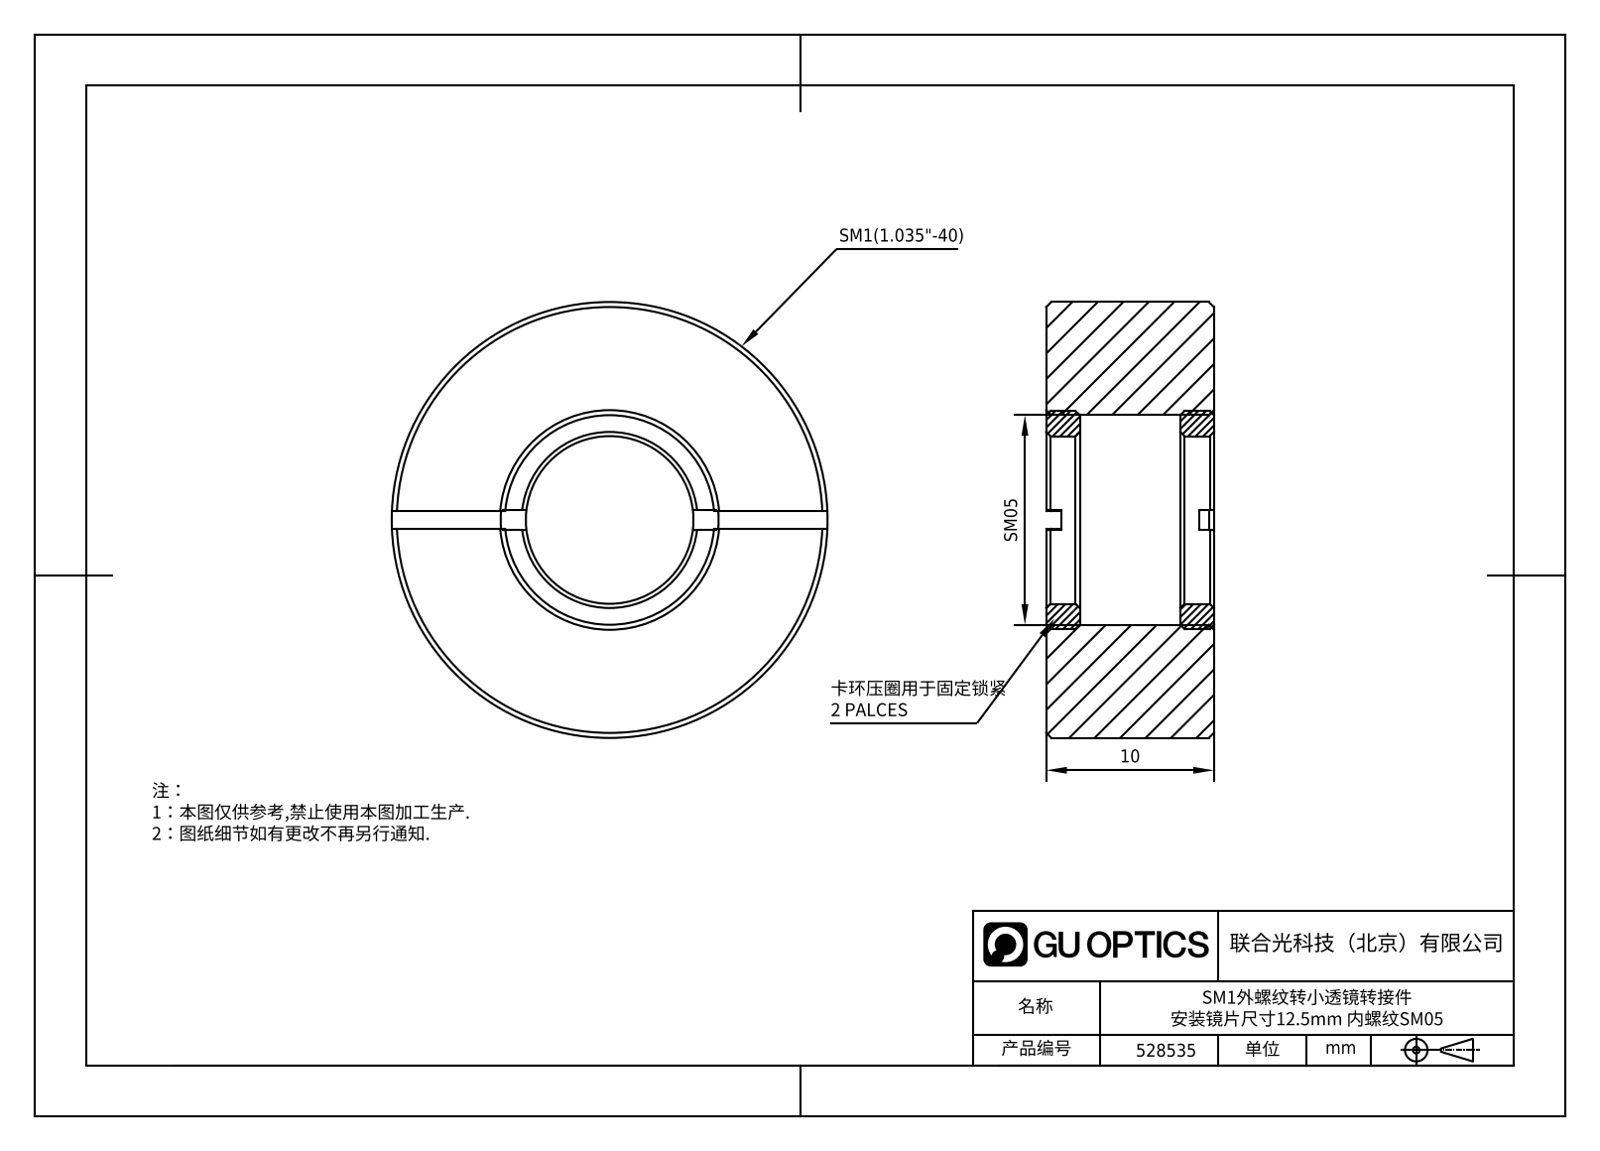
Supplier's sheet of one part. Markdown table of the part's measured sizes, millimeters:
| quantity | value |
| --- | --- |
| part name | 528535 |
| STEP written by | SolidWorks 2020 (CONFIG_CONTROL_DESIGN) |
| units | millimeters |
| bodies | 3 solids, 51 faces (27 planar, 6 cylindrical, 18 other) |
| overall size | 26 × 26 × 10 |
| volume | 4 142 mm³ |
| surface area | 2 466 mm² |
| round holes (diameter × count) | 11 × 1, 13 × 1 |
| round bosses / shafts (diameter × count) | 26 × 1, 13.59 × 1 |
| main face-to-face distances | 10, 2, 8, 6, 1, 1.1, 9, 7, 1.15, 0.9 |
